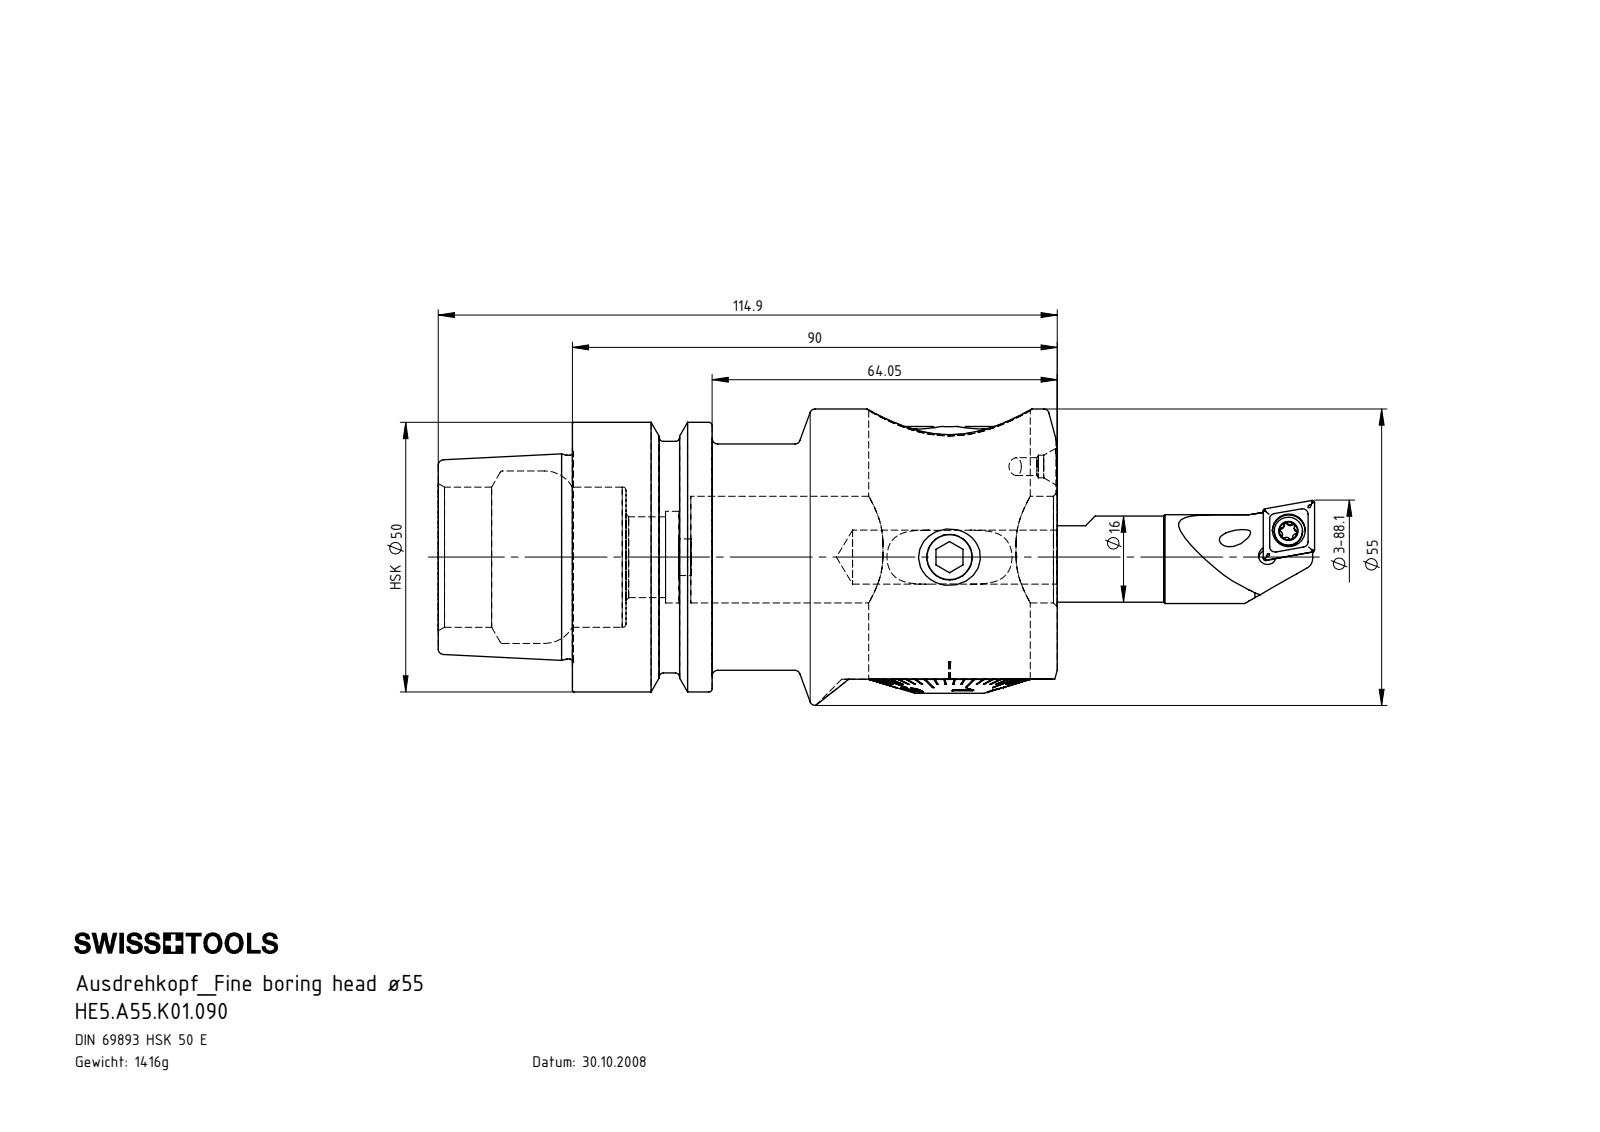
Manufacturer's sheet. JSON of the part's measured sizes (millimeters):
{"part_name": "A55-BG2.011.016_E; WCB-ER2.001.009_A; A55-BG2.013.005_C; HE5-A55.K00.090_B_Fertigbearbeitung (+8 more)", "step_written_by": "SolidWorks 2022 (AUTOMOTIVE_DESIGN)", "units": "millimeters", "bodies": {"solids": 17, "faces": 886, "planar": 348, "cylindrical": 179, "other": 359}, "overall_size": [162.65, 55, 55], "volume_mm3": 180751, "surface_area_mm2": 56169, "round_holes": [[3.3, 3], [8.5, 3], [3, 2], [1, 1], [1.6, 1], [2, 1], [4.2, 1], [4.4, 1], [6.1, 1], [6.8, 1], [8, 1], [10, 1]], "round_bosses_or_shafts": [[10, 3], [5.25, 2], [4, 2], [55, 1], [50, 1], [42.95, 1], [42, 1], [37.81, 1]], "partial_cylinders_radius": [[0.34, 12], [0.59, 12], [3.2, 3], [0.5, 1], [2, 1], [3.5, 1], [8.4, 1], [8.5, 1]], "face_to_face_distances": [22, 90, 2.5, 5.3, 6.48, 1.18, 2.8, 3.68, 16, 24.8], "hole_center_spacings": [14.5, 7.25, 0.37, 6.07, 6.19, 14.7, 15.07, 18.83]}
